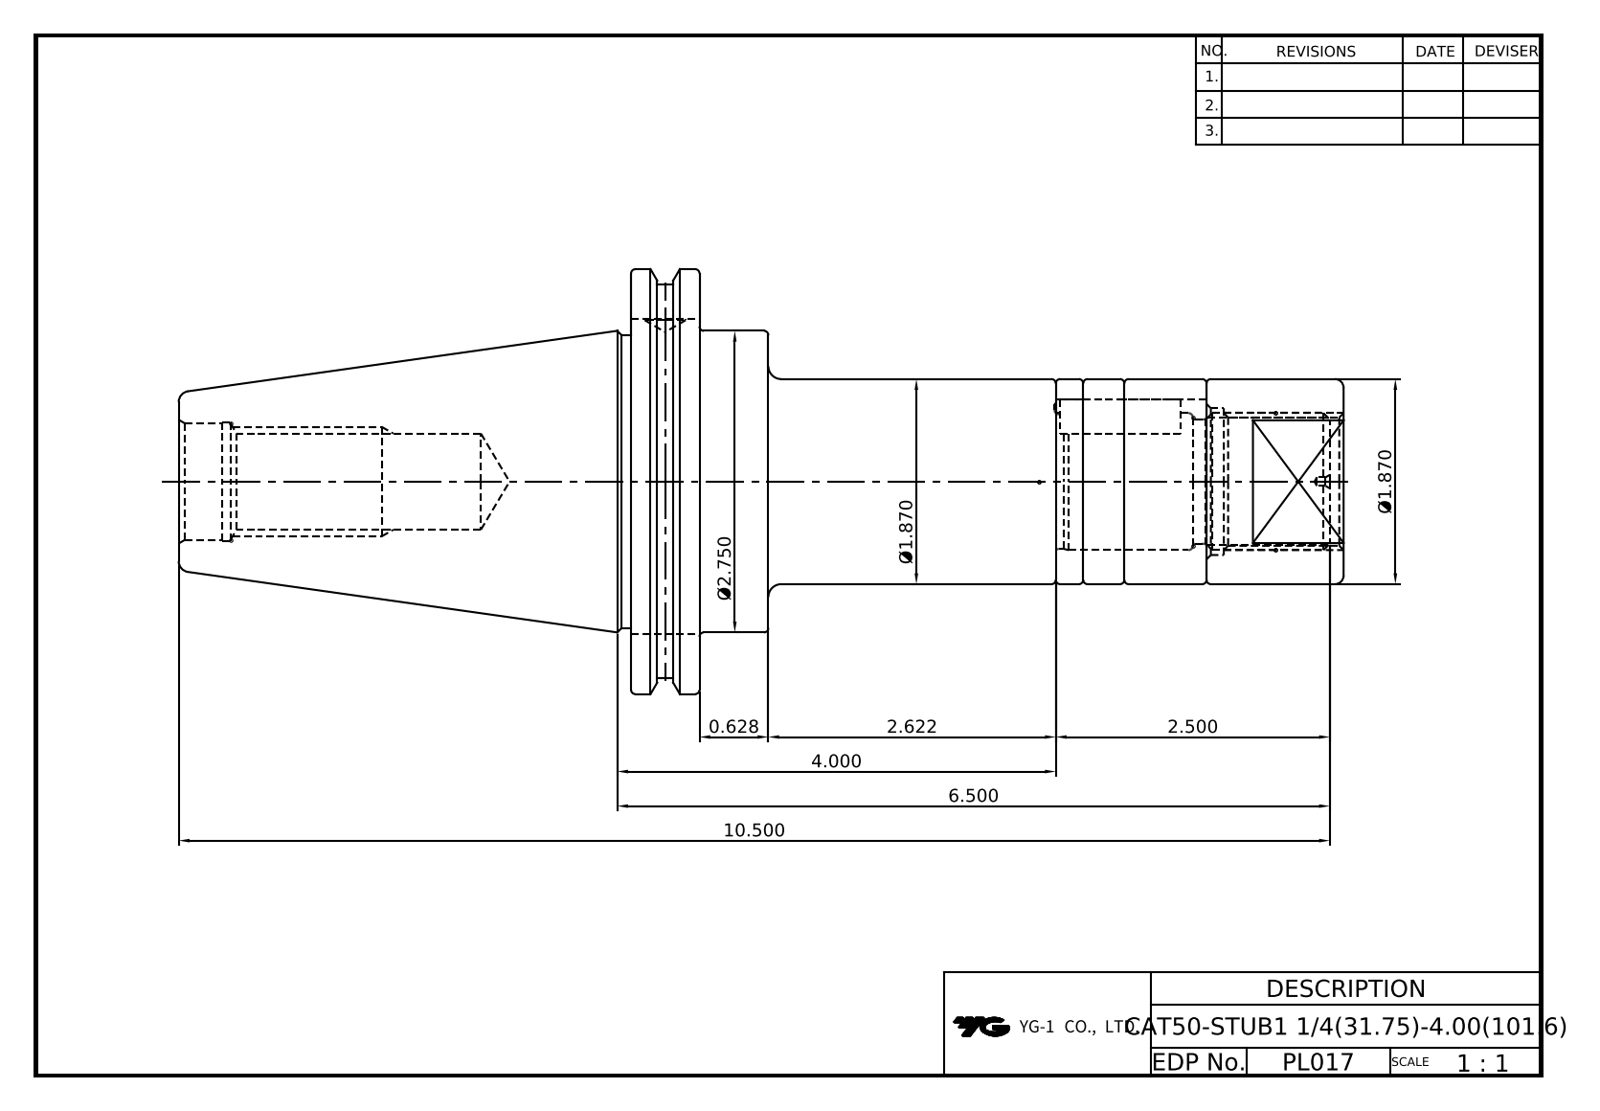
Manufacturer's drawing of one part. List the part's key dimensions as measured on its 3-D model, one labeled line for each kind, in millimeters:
Part name (STEP PRODUCT): LO-CAT50-STUB31.75-101.6; 7.938x7.938x28; COLLAR_STUB31.75(6.35T); COLLAR_STUB31.75(9.525T) (+2 more)
STEP written by: Autodesk Inventor 2025 (AP242_MANAGED_MODEL_BASED_3D_ENGINEERING_MIM_LF)
Units: millimetres
Bodies: 6 solids, 110 faces (58 planar, 27 cylindrical, 25 other)
Overall size (bounding box): 268.52 × 98.42 × 94.69
Volume: 625 531 mm³ · Surface area: 84 989 mm²
Round holes (diameter × count): ⌀9.53 ×1, ⌀21.97 ×1, ⌀26.2 ×1, ⌀29.46 ×1, ⌀31.75 ×1
Round bosses / shafts (diameter × count): ⌀98.42 ×1, ⌀91.29 ×1, ⌀69.85 ×1, ⌀69.25 ×1, ⌀47.5 ×1, ⌀46 ×1, ⌀29 ×1
Partial cylindrical surfaces — rounded edges, fillets, slot ends (radius × count): R3.97 ×2
Main face-to-face distances: 15.88, 31.83, 15.95, 33.58, 98.43, 82.55, 66.6, 132.01, 116.13, 100.18
